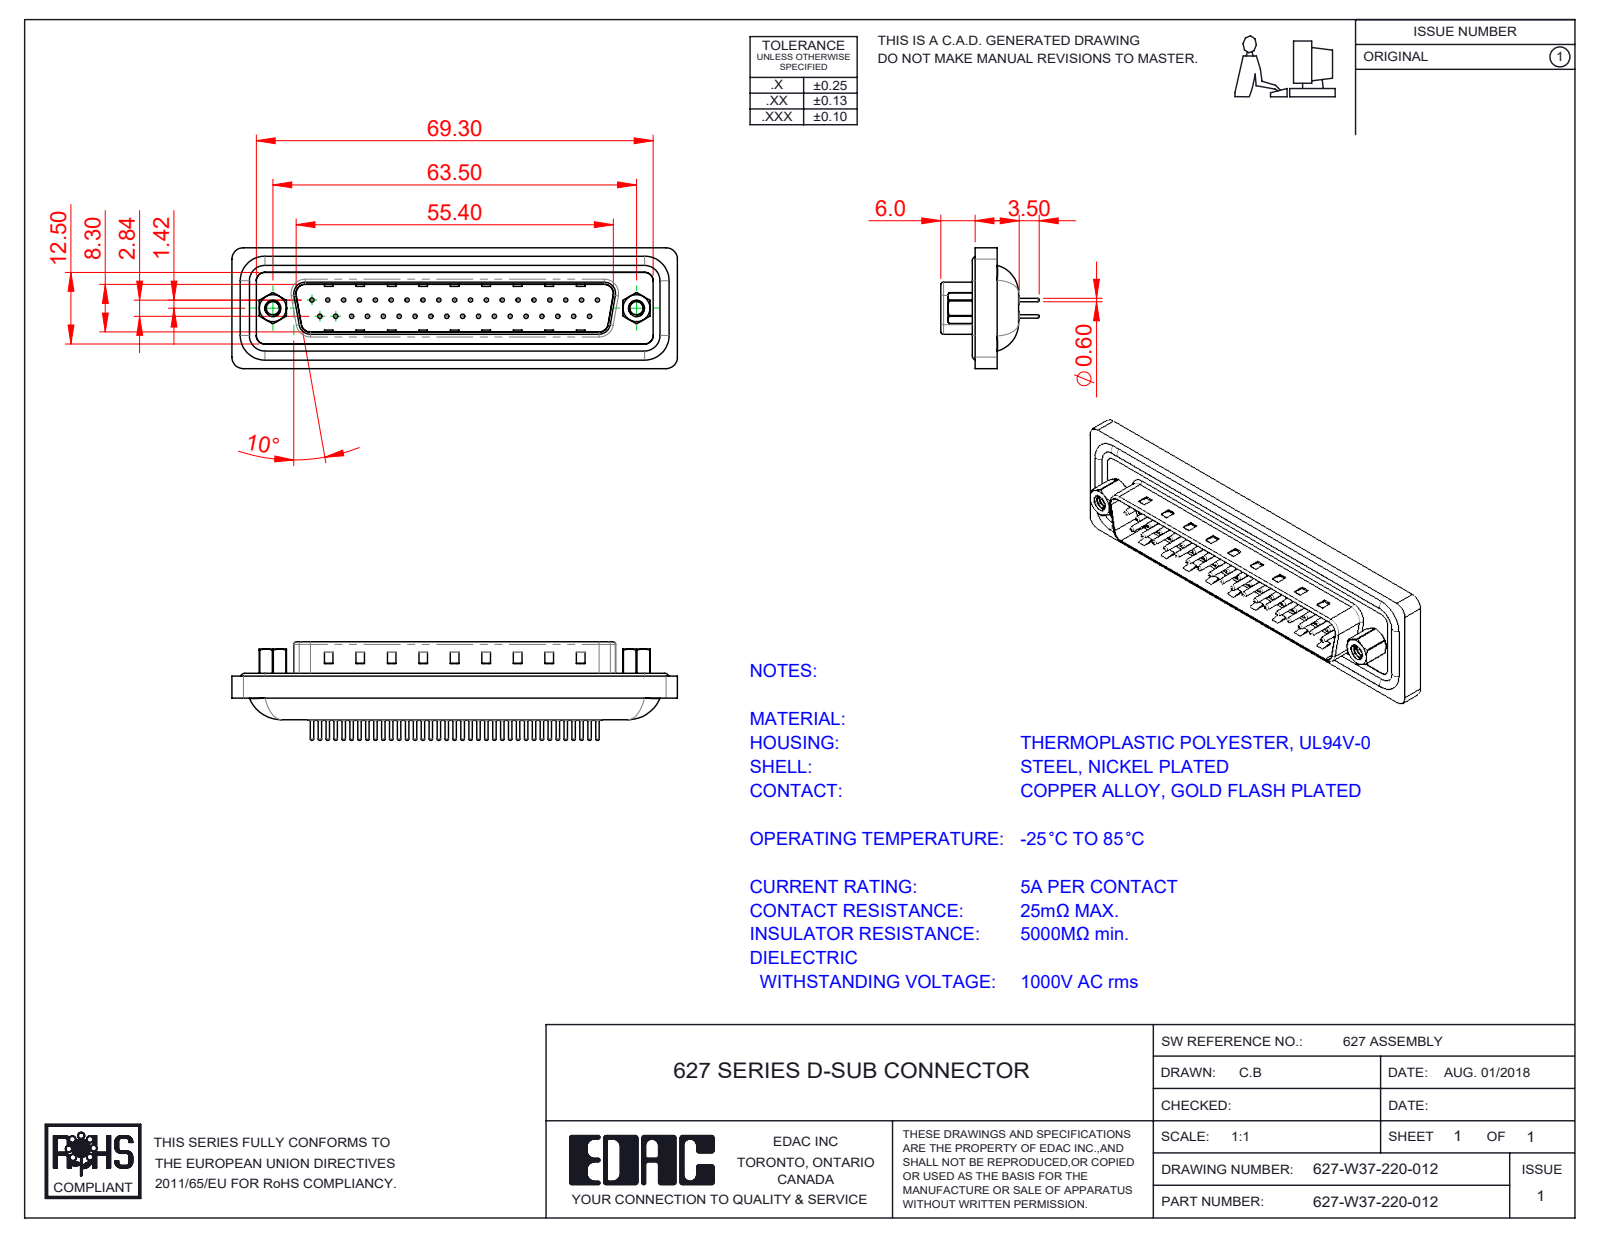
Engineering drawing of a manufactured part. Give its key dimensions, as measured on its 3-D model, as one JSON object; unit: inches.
{"part_name": "627W Housing_37 Contacts; 627W Contact Row 1_20; 627W 4-40 Threaded Rivet; 627W Shell Front_37 Contacts (+4 more)", "step_written_by": "SolidWorks 2023 (CONFIG_CONTROL_DESIGN)", "units": "inches", "bodies": {"solids": 45, "faces": 1999, "planar": 496, "cylindrical": 816, "other": 687}, "overall_size": [3.063, 0.831, 0.685], "volume_in3": 0.583, "surface_area_in2": 22.29, "round_holes": [[0.03, 37], [0.059, 37], [0.063, 37], [0.079, 37], [0.089, 2], [0.09, 2], [0.157, 2], [0.189, 2], [0.197, 2]], "round_bosses_or_shafts": [[0.024, 37], [0.059, 9], [0.063, 4], [0.193, 2], [0.11, 2]], "partial_cylinders_radius": [[0.079, 16], [0.059, 14], [0.02, 8], [0.106, 6], [0.035, 4], [0.063, 4], [0.169, 4], [0.016, 2]], "face_to_face_distances": [0.03, 0.016, 0.161, 0.043, 0.108, 0.181, 0.148, 0.222, 0.608, 0.579], "hole_center_spacings": [0.124, 0.109, 0.218, 0.327, 0.198, 0.398, 0.436, 0.503]}
